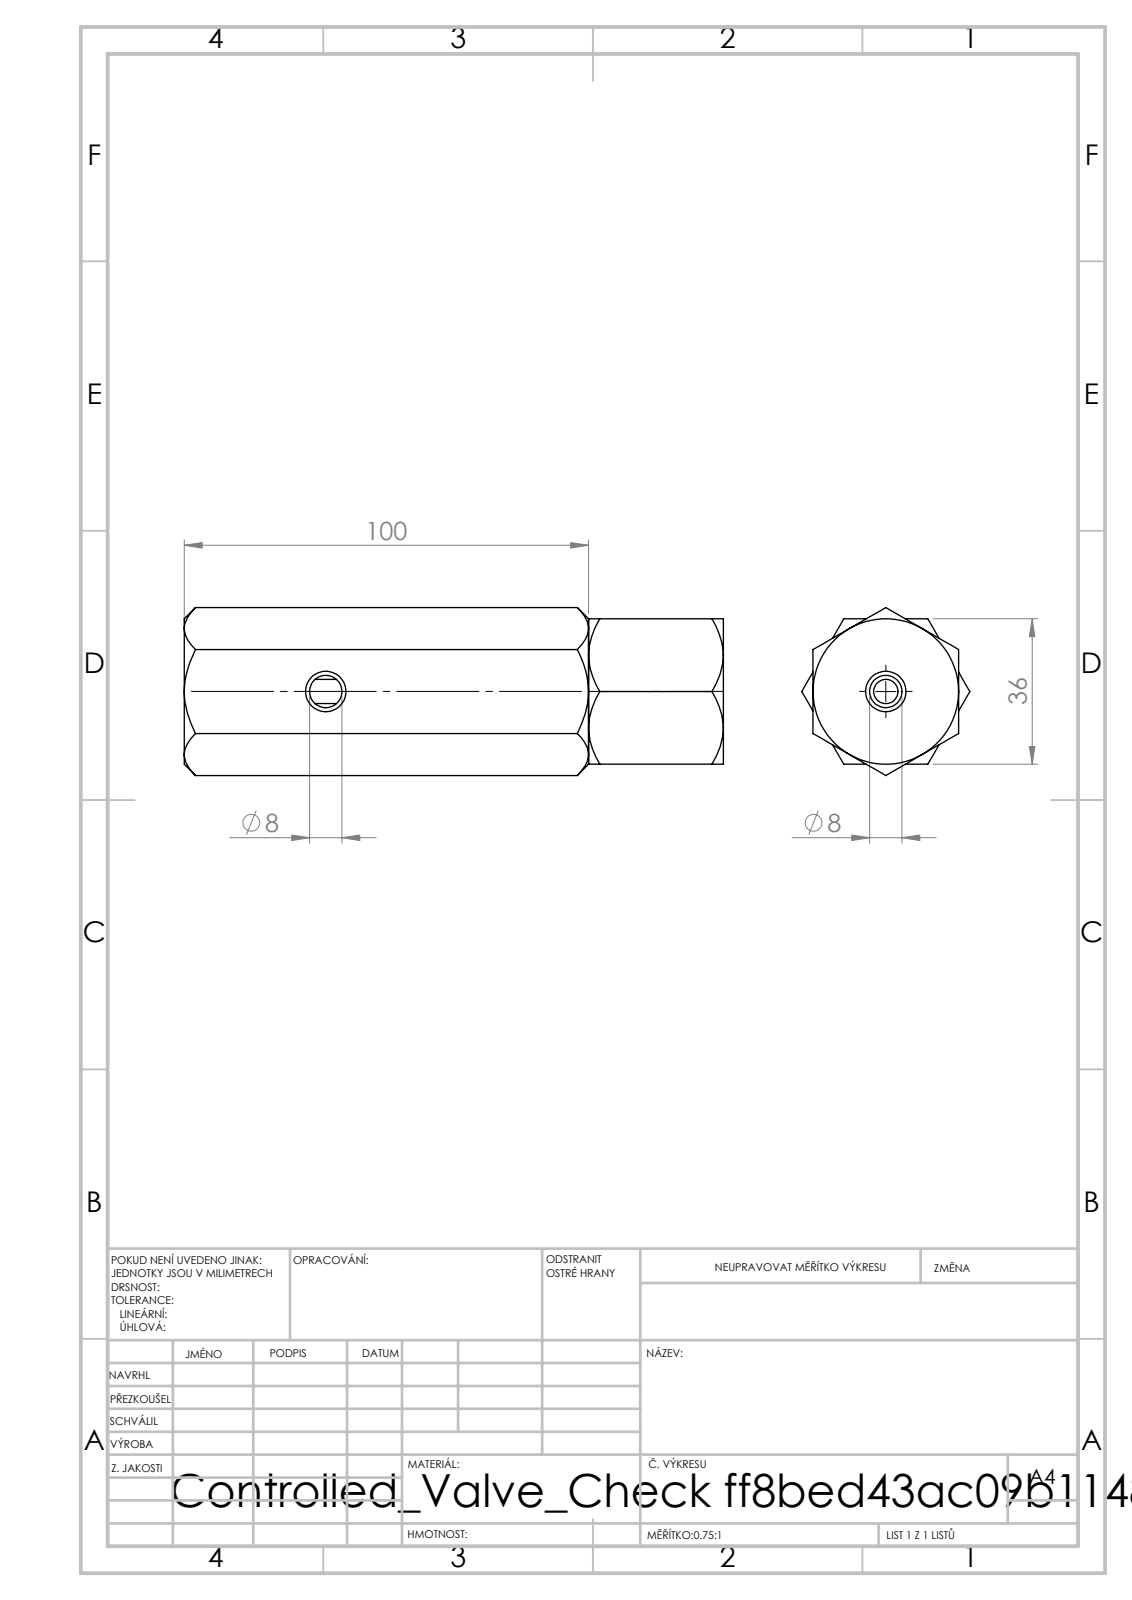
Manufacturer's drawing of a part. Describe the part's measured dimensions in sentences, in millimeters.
Its 3-D file was written by "SolidWorks 2019 (CONFIG_CONTROL_DESIGN)". It is 2 solids with 59 faces: 19 planar, 8 cylindrical and 32 other. Overall it measures 133.33 by 41.57 by 41.57 millimeters. Its volume is 142 568 cubic millimeters and its surface area 23 929 square millimeters. Round holes: 2 of diameter 8, 1 of diameter 6, 1 of diameter 10. The main face-to-face distances are 36, 100, 33.33, 133.33, 113.33, 80, 20, 18.
